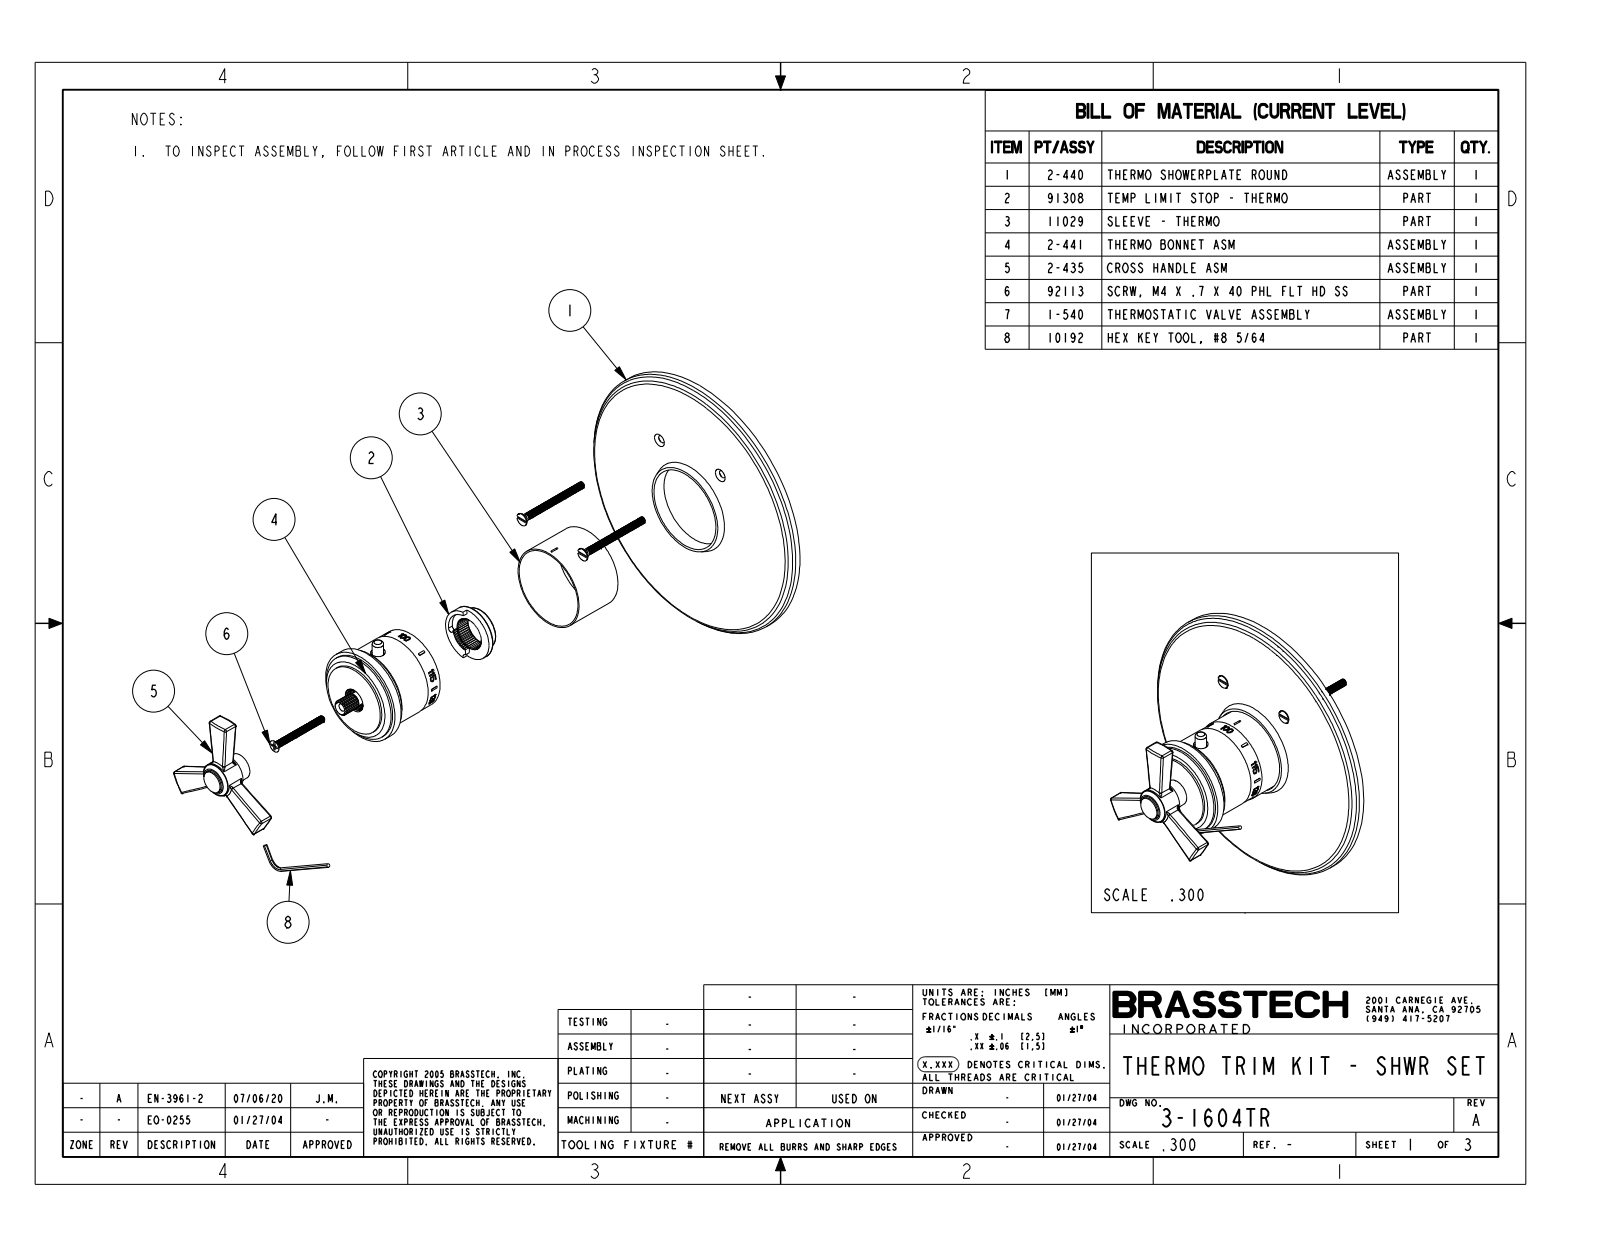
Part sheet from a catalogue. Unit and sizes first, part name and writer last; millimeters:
Units: millimetres
Overall size (bounding box): 165.1 × 165.1 × 94.1
Round bosses / shafts (diameter × count): ⌀165.1 ×1, ⌀56.9 ×1, ⌀53.1 ×1, ⌀50 ×1, ⌀49.3 ×1, ⌀49 ×1, ⌀42.9 ×1, ⌀20.3 ×1
Partial cylindrical surfaces — rounded edges, fillets, slot ends (radius × count): R1 ×6, R2.5 ×6, R24.6 ×1
Main face-to-face distances: 8, 70.9, 63, 5.1, 1.3, 69.6, 61.7, 3.8, 60.8, 65.8
Volume: 308 600 mm³ · Surface area: 61 670 mm²
Bodies: 1 solid, 496 faces (343 planar, 57 cylindrical, 96 other)
Part name (STEP PRODUCT): 3-1604TR
STEP written by: CREO PARAMETRIC BY PTC INC, 2018400 (CONFIG_CONTROL_DESIGN)
